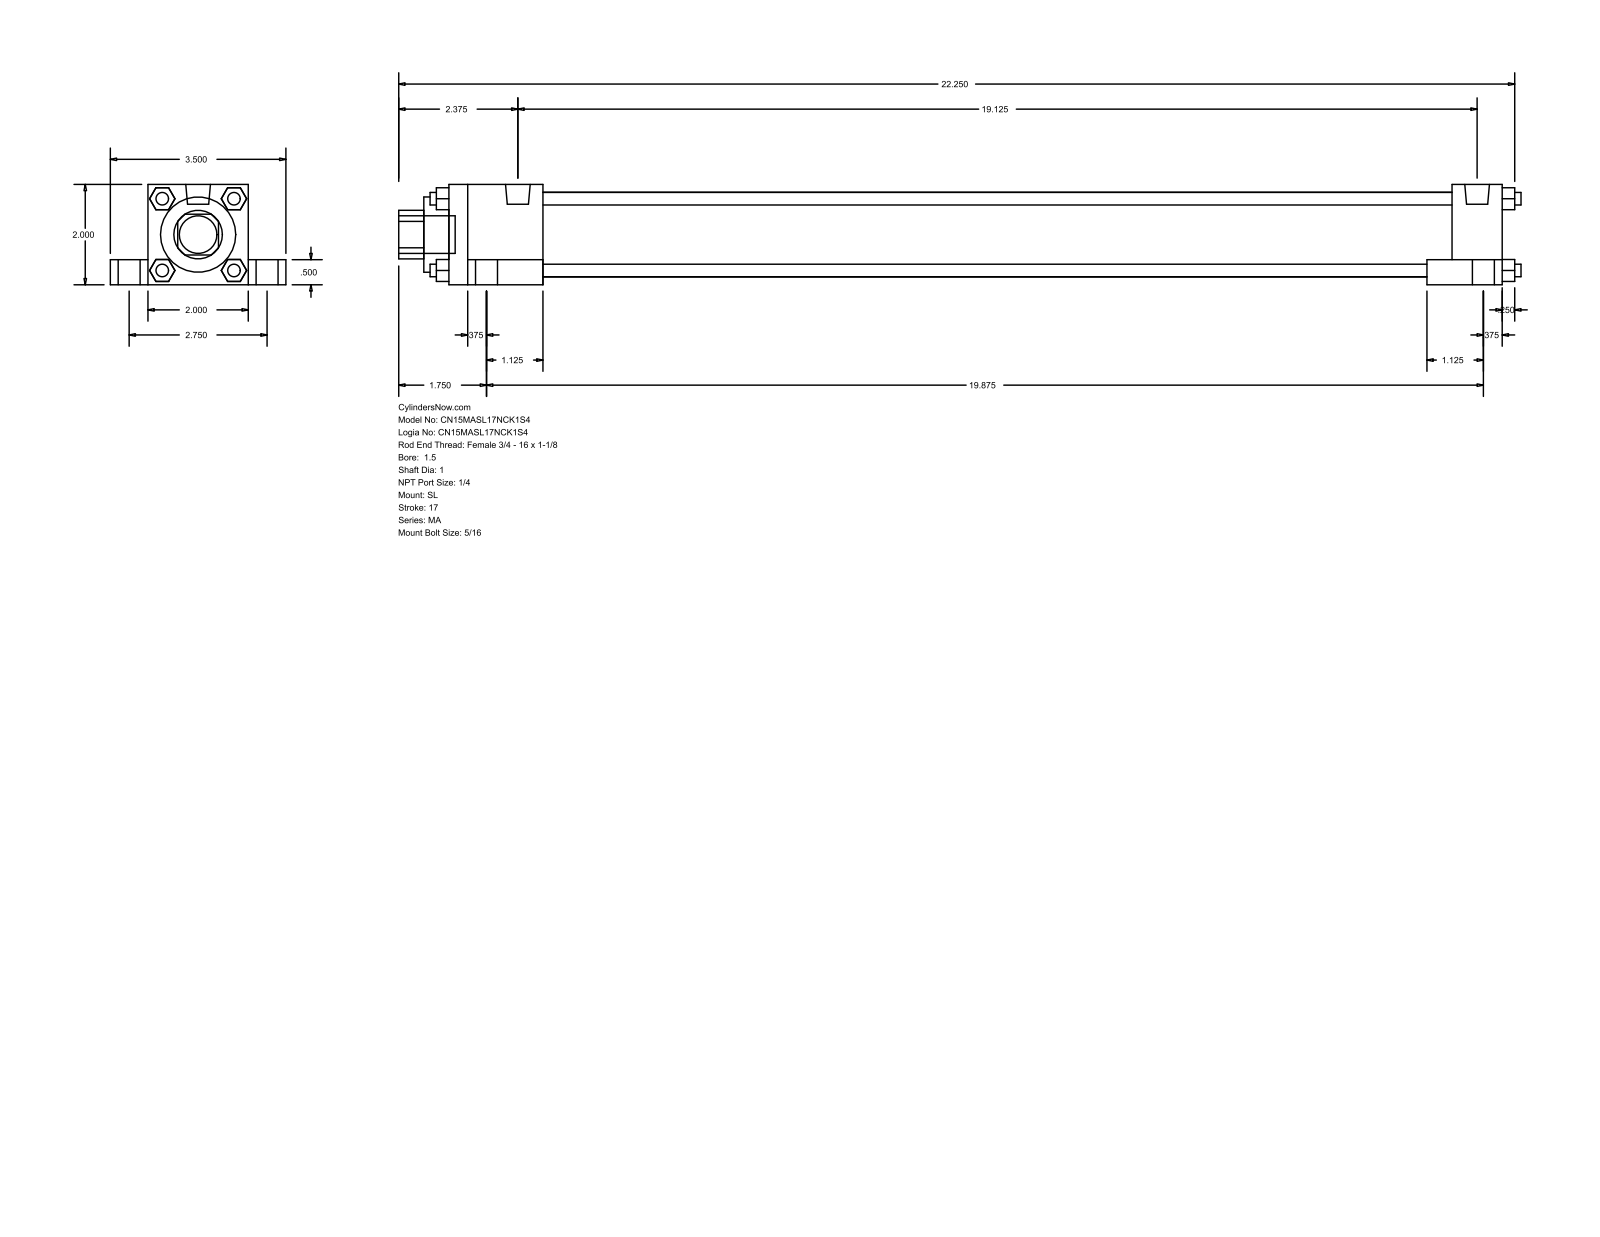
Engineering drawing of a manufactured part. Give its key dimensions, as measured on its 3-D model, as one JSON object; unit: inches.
{"part_name": "MA_SL__0150_1", "step_written_by": "GSSL Pune (CONFIG_CONTROL_DESIGN)", "units": "inches", "bodies": {"solids": 0, "faces": 148, "planar": 112, "cylindrical": 36, "other": 0}, "overall_size": [22.375, 3.5, 2], "round_holes": [[1, 1], [1.5, 1], [1.69, 1]], "round_bosses_or_shafts": [[0.687, 4], [0.437, 4], [0.313, 4], [0.25, 4], [0.492, 2], [0.75, 1]], "partial_cylinders_radius": [[0.484, 1]], "face_to_face_distances": [2, 0.5, 0.75, 2.75, 0.375, 1.5, 0.25, 21, 1, 20]}
